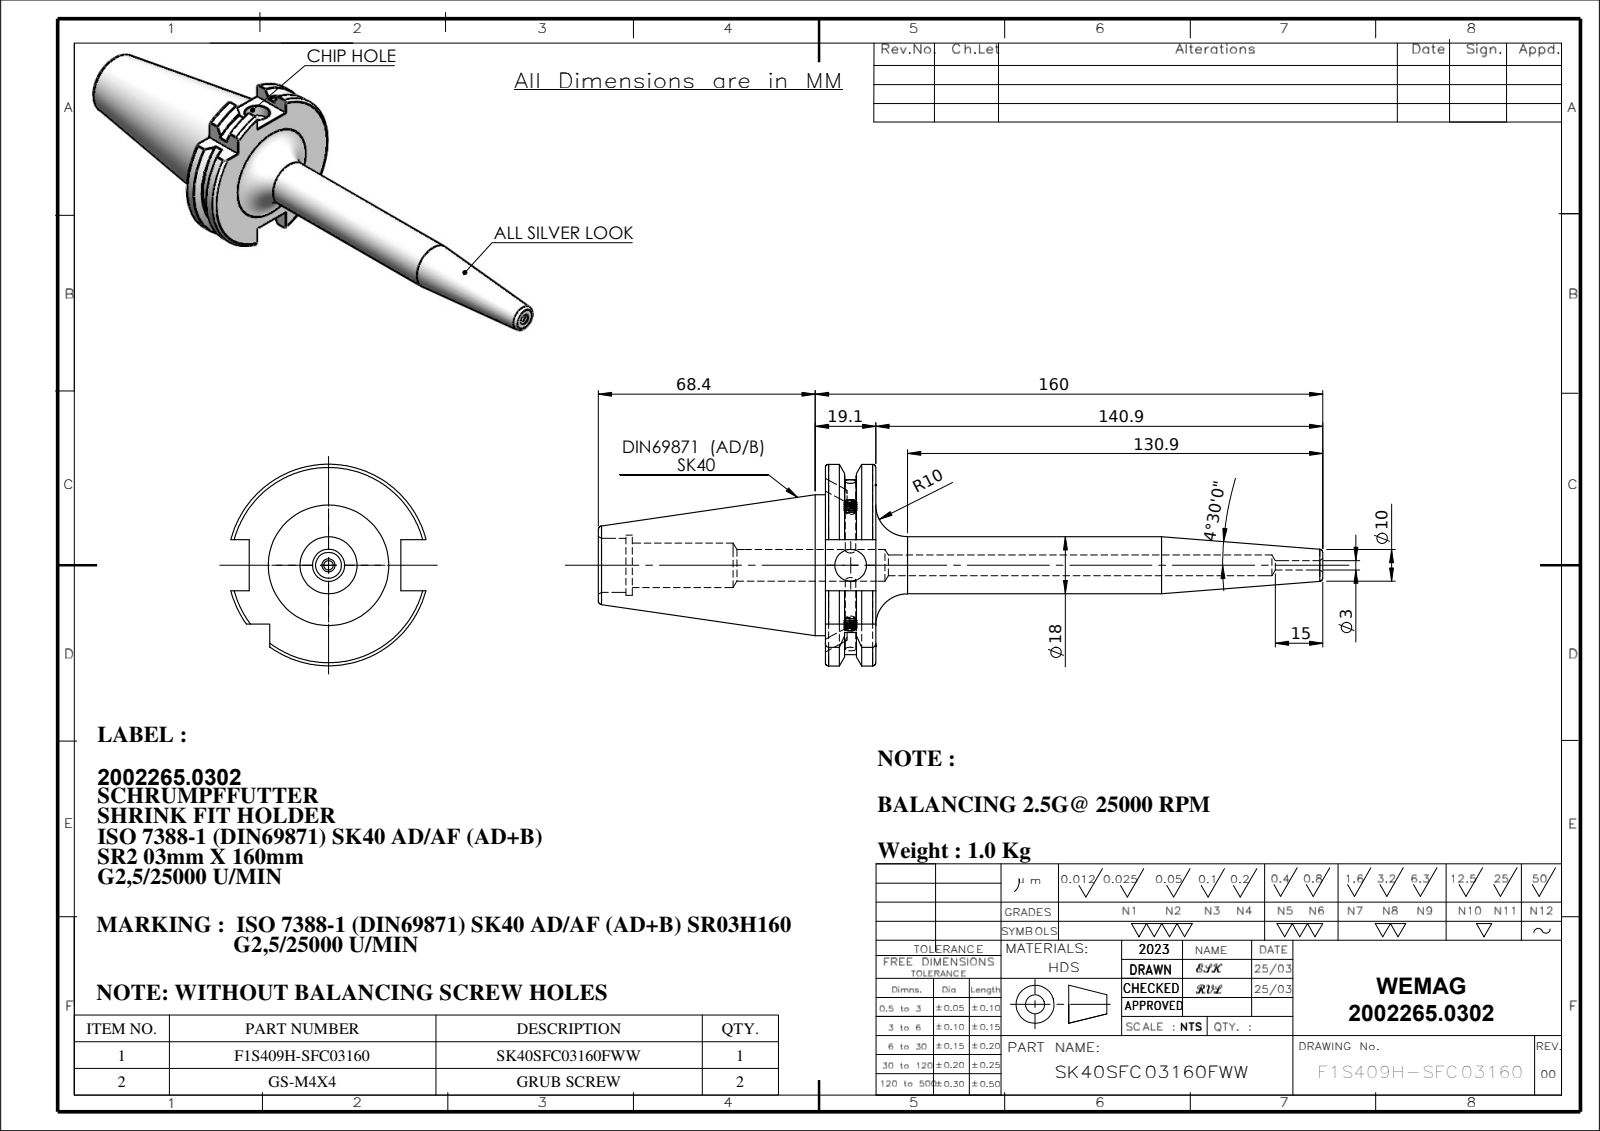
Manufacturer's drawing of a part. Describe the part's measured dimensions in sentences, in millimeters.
The part is named "91406-SR203160; SK40SFC03160FWW; GS-M4X4_DIN 913 - M4 x 4-N". Its 3-D file was written by "SolidWorks 2018 (CONFIG_CONTROL_DESIGN)". It is 3 solids with 196 faces: 46 planar, 54 cylindrical and 96 other. Overall it measures 228.4 by 63.55 by 61.48 millimeters. Its volume is 129 730 cubic millimeters and its surface area 30 861 square millimeters. Round holes: 2 of diameter 10, 1 of diameter 2.99, 1 of diameter 3.3, 1 of diameter 6.5, 1 of diameter 14, 1 of diameter 17, 1 of diameter 19. Round bosses or shafts: 2 of diameter 4, 1 of diameter 44.45, 1 of diameter 18. Partial cylindrical surfaces (rounded edges, fillets, slot ends): 1 of radius 28.12, 1 of radius 31.77. The main face-to-face distances are 15.9, 16.1, 47.8, 71.6, 87.5, 10.7, 60.9, 76.8, 77.63, 66.93.
